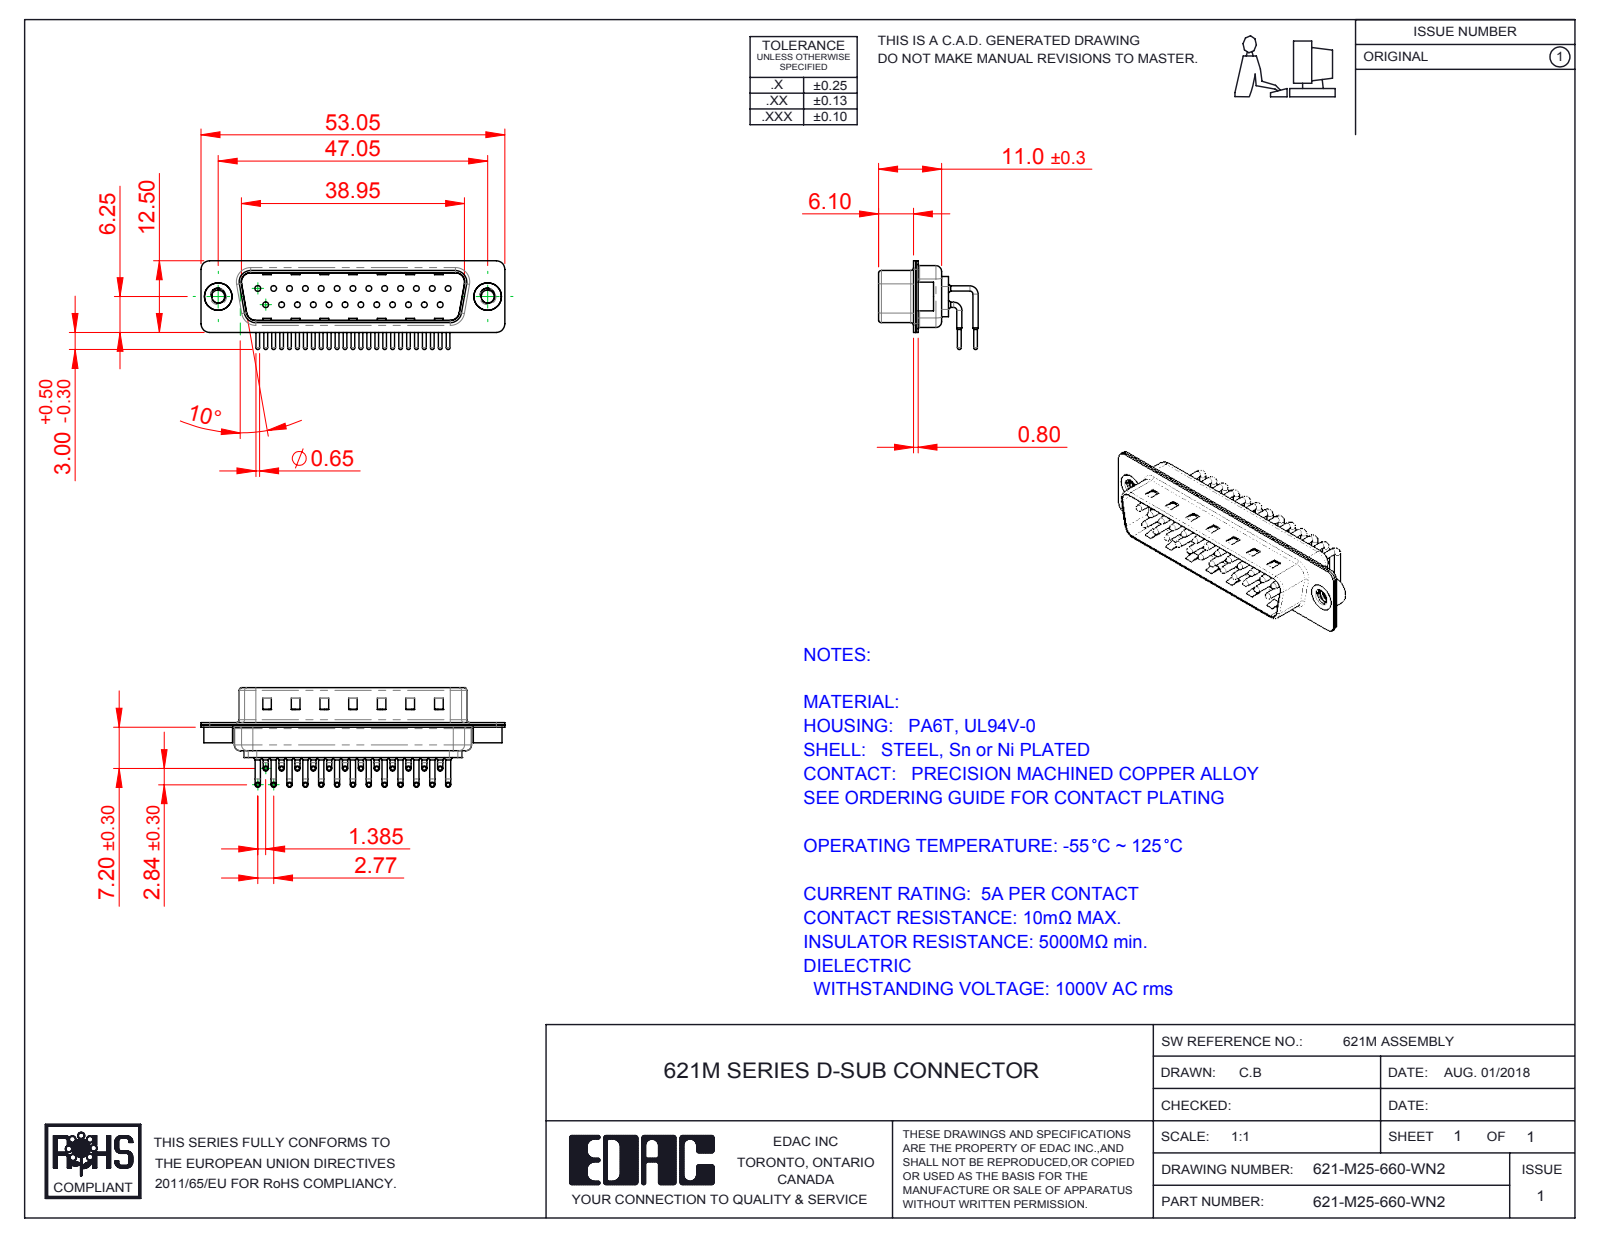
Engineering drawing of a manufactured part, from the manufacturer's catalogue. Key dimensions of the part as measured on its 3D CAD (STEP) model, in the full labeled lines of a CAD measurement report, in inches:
Part name (STEP PRODUCT): 621M Shell Rear_25 Contacts; 621-M25-660-WN2; 621M 4-40 Threaded Rivet; 621M Contact Row 2 (+3 more)
STEP written by: SolidWorks 2016 (CONFIG_CONTROL_DESIGN)
Units: inches
Bodies: 30 solids, 3126 faces (1771 planar, 1037 cylindrical, 318 other)
Overall size (bounding box): 2.089 × 0.685 × 0.61
Volume: 0.175 in³ · Surface area: 11.76 in²
Round holes (diameter × count): ⌀0.039 ×25, ⌀0.067 ×25, ⌀0.079 ×25, ⌀0.089 ×2, ⌀0.157 ×2, ⌀0.189 ×2
Round bosses / shafts (diameter × count): ⌀0.035 ×50, ⌀0.059 ×25, ⌀0.026 ×25, ⌀0.197 ×2, ⌀0.193 ×2
Partial cylindrical surfaces — rounded edges, fillets, slot ends (radius × count): R0.04 ×25, R0.059 ×16, R0.079 ×12, R0.02 ×8, R0.063 ×8, R0.01 ×4, R0.024 ×4, R0.026 ×4
Main face-to-face distances: 0.016, 0.033, 0.376, 0.343, 0.049, 0.409, 0.059, 0.075, 0.014, 0.24
Hole centre spacings: 0.124, 0.327, 0.109, 0.218, 0.436, 0.654, 0.198, 0.198
